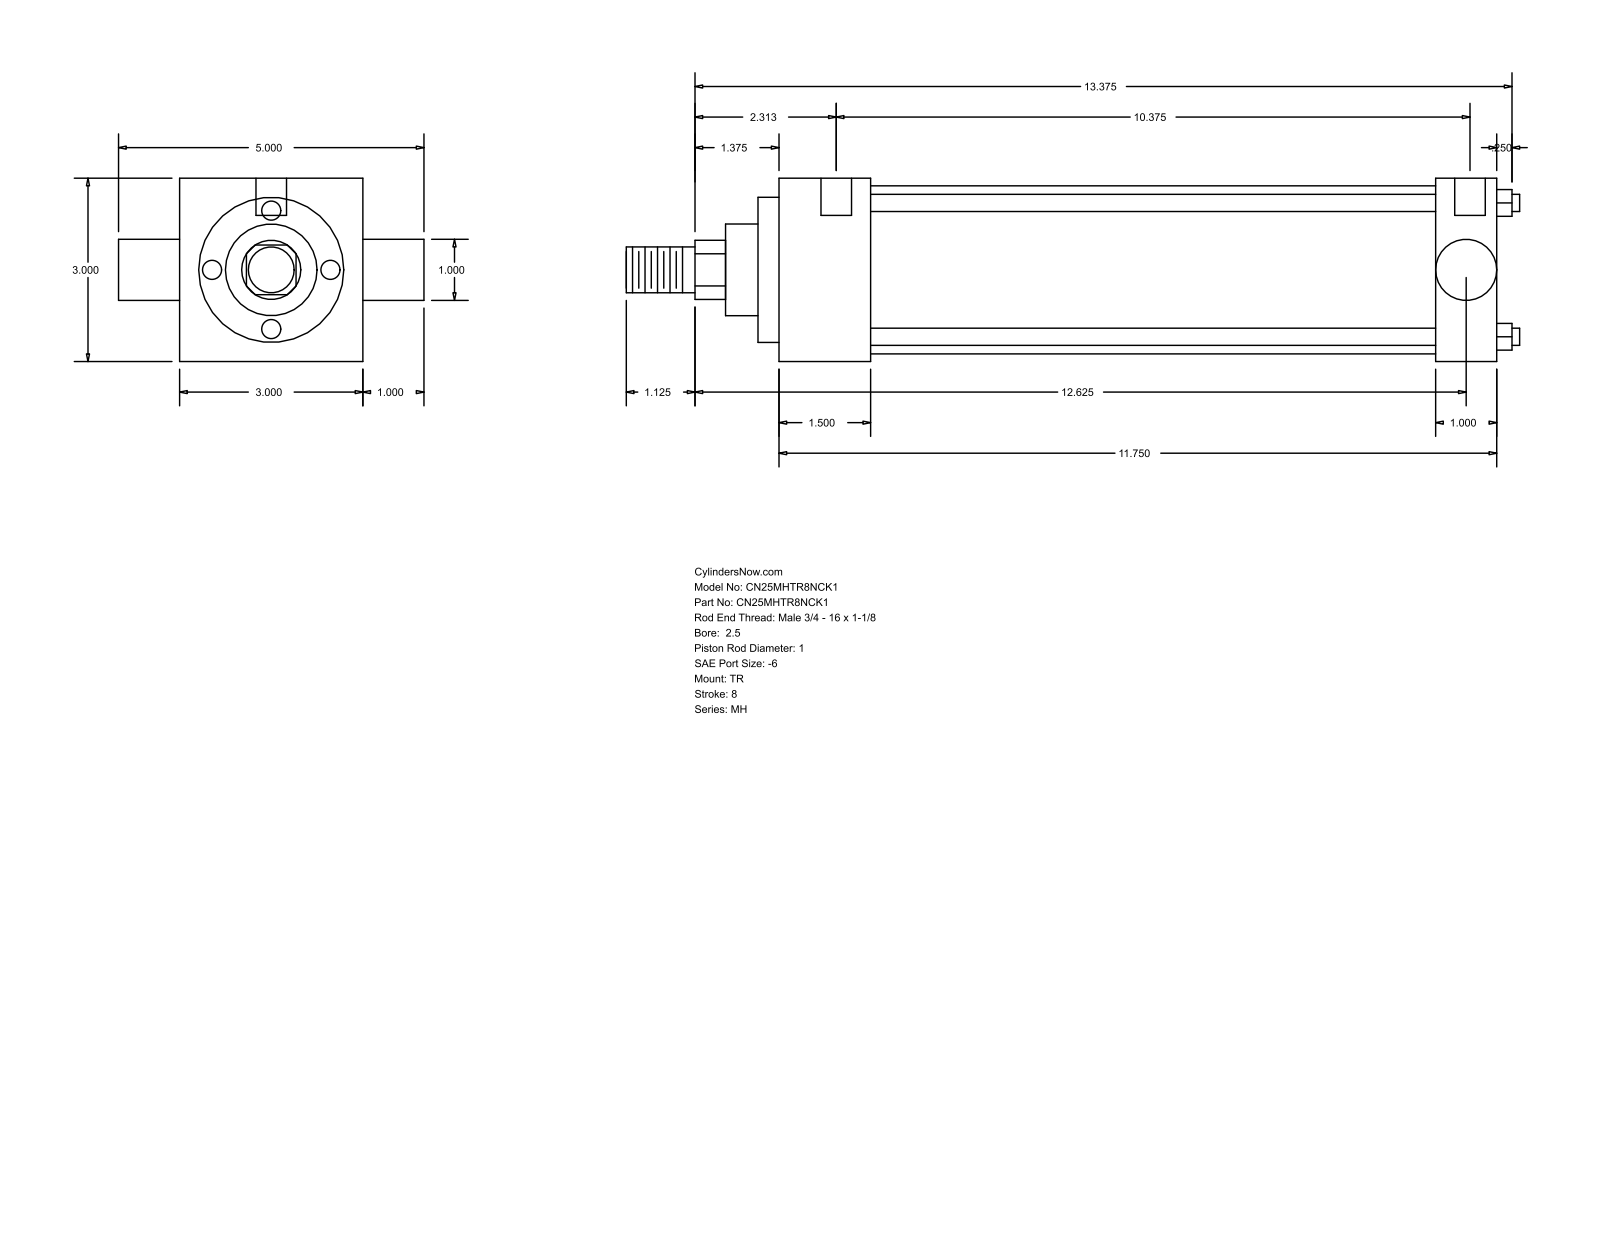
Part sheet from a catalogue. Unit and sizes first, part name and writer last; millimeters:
Units: millimetres
Overall size (bounding box): 371.48 × 127 × 76.2
Round holes (diameter × count): ⌀5.56 ×3, ⌀12.7 ×2
Round bosses / shafts (diameter × count): ⌀7.14 ×4, ⌀69.85 ×1, ⌀60.33 ×1, ⌀38.1 ×1, ⌀25.4 ×1, ⌀25.35 ×1, ⌀19.05 ×1
Partial cylindrical surfaces — rounded edges, fillets, slot ends (radius × count): R12.29 ×1
Main face-to-face distances: 76.2, 298.46, 25.4, 38.11, 260.35, 273.06, 234.95, 8.73, 46.84, 281.79
Hole centre spacings: 3.18, 4.76, 263.52, 266.7, 268.28, 271.46
Bodies: 0 solids, 86 faces (61 planar, 25 cylindrical, 0 other)
Part name (STEP PRODUCT): MH_TR__0250_1
STEP written by: GSSL Pune (CONFIG_CONTROL_DESIGN)
